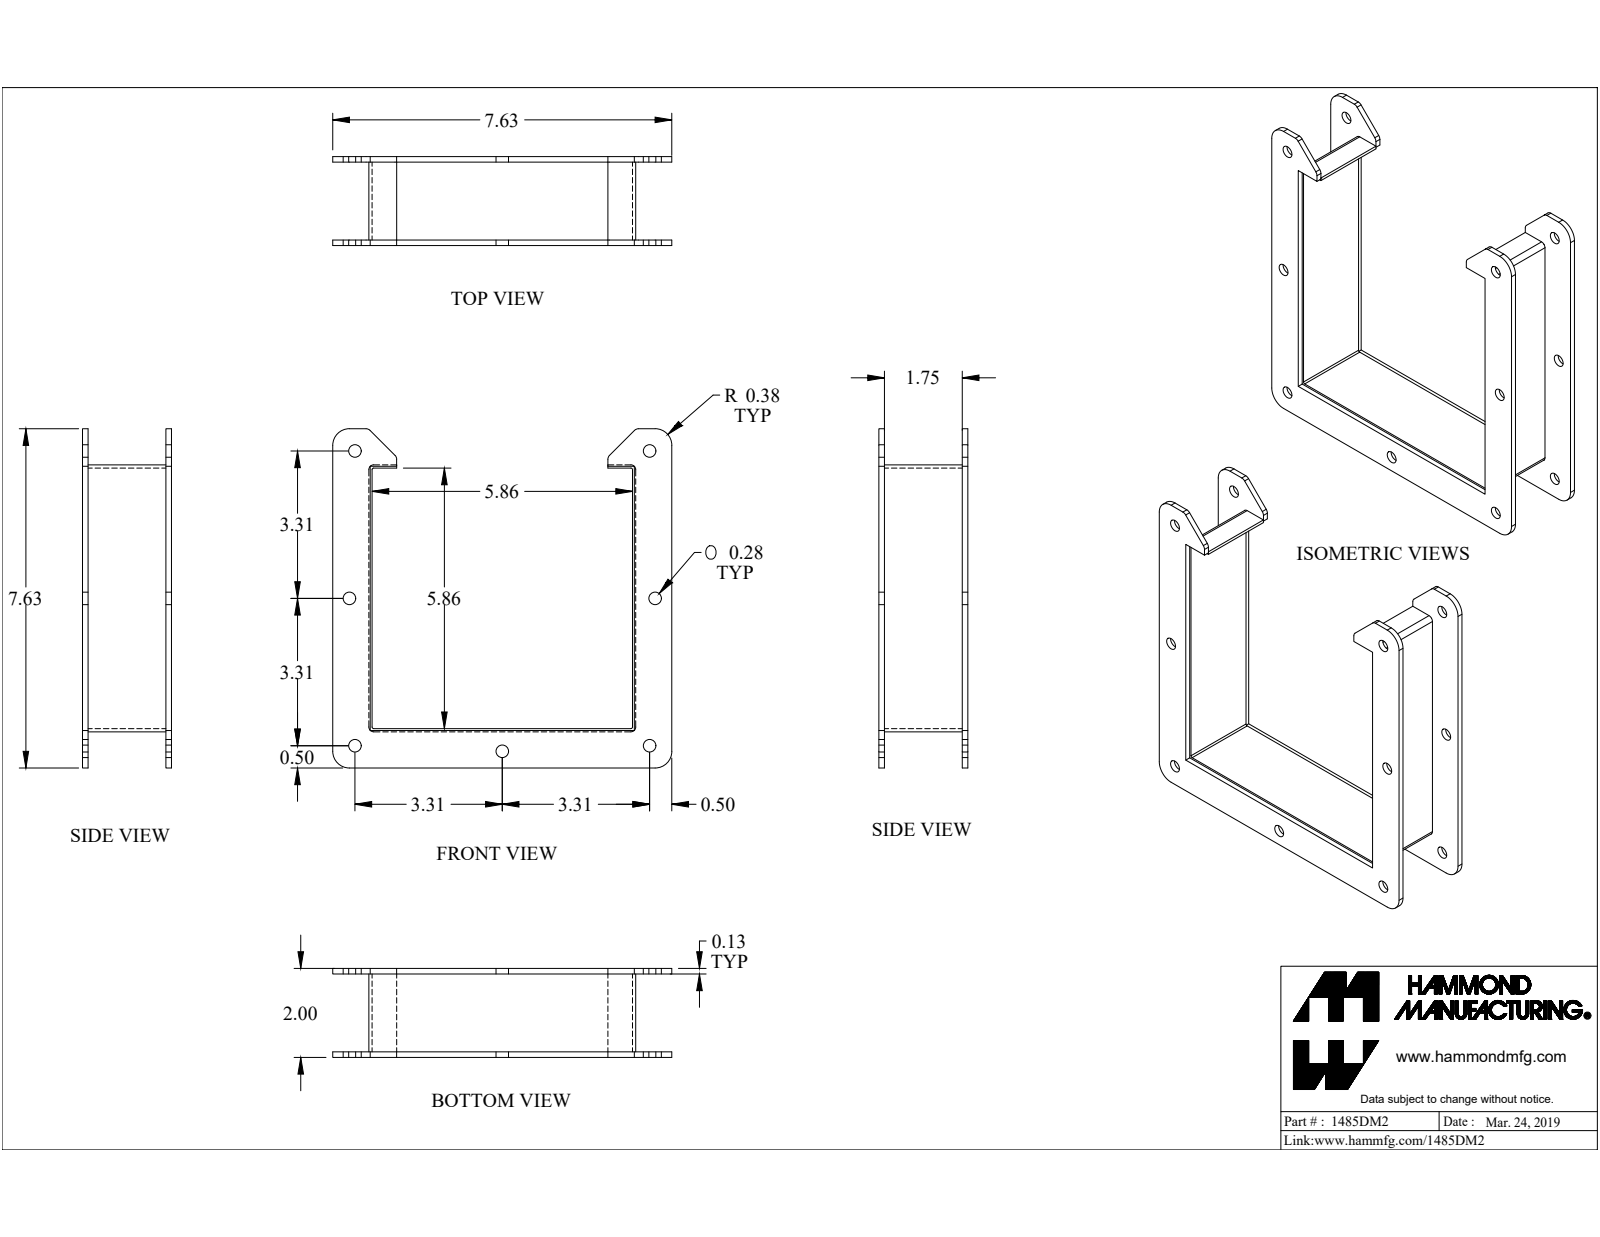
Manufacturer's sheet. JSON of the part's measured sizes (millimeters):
{"part_name": "1485DM2", "step_written_by": "SolidWorks 2019 (CONFIG_CONTROL_DESIGN)", "units": "millimeters", "bodies": {"solids": 3, "faces": 84, "planar": 46, "cylindrical": 38, "other": 0}, "overall_size": [193.7, 193.7, 50.8], "volume_mm3": 112300, "surface_area_mm2": 98900, "round_holes": [[7.1, 7]], "partial_cylinders_radius": [[0.9, 4], [2.7, 4], [3.2, 4], [9.5, 4]], "face_to_face_distances": [1.8, 150.6, 47.6, 3.2, 47.6, 50.8, 44.5, 3.2, 152.4, 148.7], "hole_center_spacings": [191, 168.3, 84.2, 84.2, 238, 123.5, 123.5, 174.6]}
